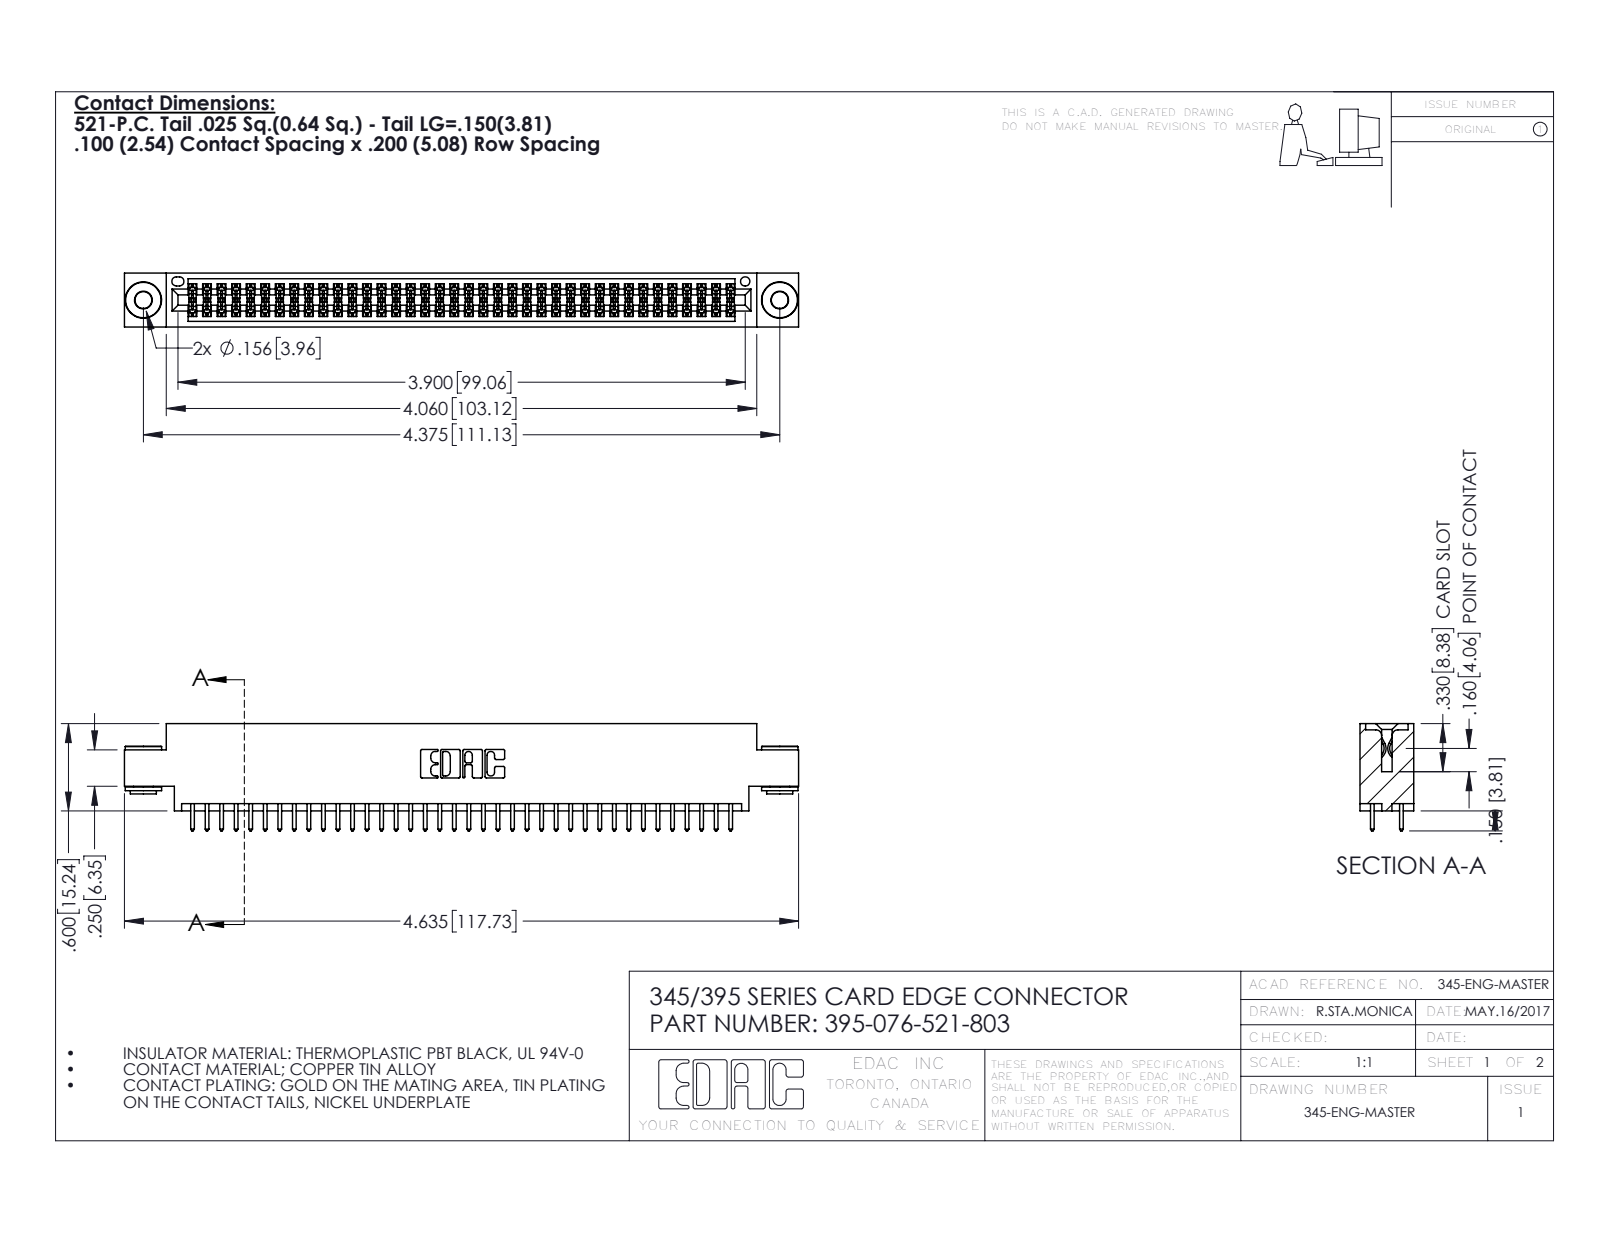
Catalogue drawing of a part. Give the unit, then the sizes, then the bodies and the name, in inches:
Units: inches
Overall size (bounding box): 4.635 × 0.737 × 0.37
Round holes (diameter × count): ⌀0.116 ×2, ⌀0.156 ×2, ⌀0.064 ×1
Round bosses / shafts (diameter × count): ⌀0.25 ×2, ⌀0.18 ×2, ⌀0.136 ×2
Partial cylindrical surfaces — rounded edges, fillets, slot ends (radius × count): R0.006 ×114, R0.01 ×76, R0.01 ×22, R0.007 ×6, R0.031 ×6, R0.026 ×3, R0.014 ×2, R0.019 ×2
Main face-to-face distances: 0.072, 0.298, 0.37, 0.2, 0.098, 0.272, 0.025, 0.225, 0.175, 0.149
Hole centre spacings: 0.27, 4.139, 4.375
Volume: 0.688 in³ · Surface area: 25.94 in²
Bodies: 79 solids, 3968 faces (2602 planar, 1358 cylindrical, 8 other)
Part name (STEP PRODUCT): 345-250-002_345-250-002-102; 345-292-001_345-293-121; 395-076-521-803; 345 Part_0.170 Offset - 0.156 Dia-TH
STEP written by: SolidWorks 2016 (CONFIG_CONTROL_DESIGN)
